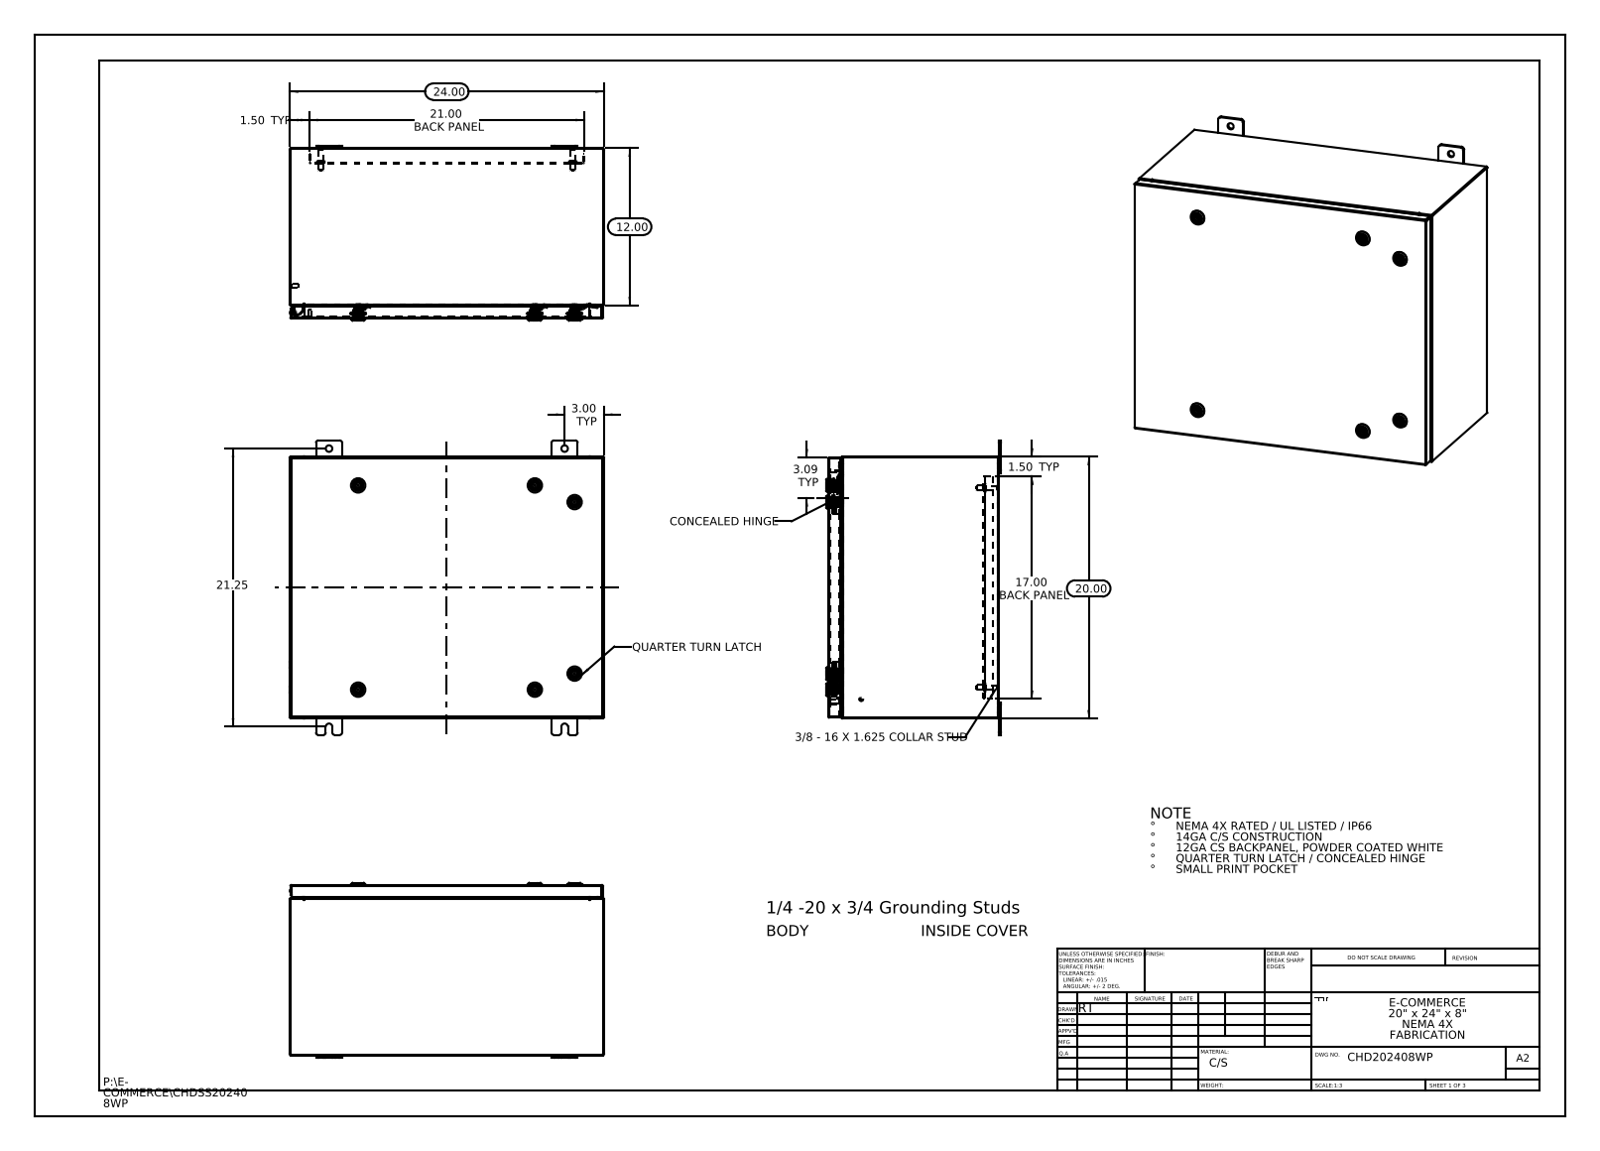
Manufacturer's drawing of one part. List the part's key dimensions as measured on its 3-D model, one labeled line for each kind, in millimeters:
Part name (STEP PRODUCT): HW-CLH-R001-0500_2412-026240-2445-Industrilas; Nut-211301-IB-Industrilas_Nut-211301-IB-Industrilas; HW-CLH-E5-8004_Cam-232112-U-Industrilas; CHDSS202408WP Body (+8 more)
STEP written by: SolidWorks 2013 (CONFIG_CONTROL_DESIGN)
Units: millimetres
Bodies: 55 solids, 5420 faces (1592 planar, 1692 cylindrical, 2136 other)
Overall size (bounding box): 609.6 × 571.5 × 339.2
Volume: 3 520 000 mm³ · Surface area: 3 497 000 mm²
Round holes (diameter × count): ⌀12.7 ×8, ⌀5 ×6, ⌀10 ×6, ⌀10.2 ×6, ⌀16 ×6, ⌀20 ×6, ⌀3.5 ×4, ⌀5.4 ×2
Round bosses / shafts (diameter × count): ⌀6 ×8, ⌀28 ×6, ⌀19.8 ×6, ⌀15.9 ×6, ⌀15.5 ×6, ⌀13.5 ×6, ⌀10 ×6, ⌀2.9 ×6
Partial cylindrical surfaces — rounded edges, fillets, slot ends (radius × count): R0.2 ×198, R3 ×198, R0.7 ×72, R0.5 ×24, R4.8 ×24, R5 ×24, R0.3 ×20, R2.2 ×18
Main face-to-face distances: 1.9, 506.1, 1.9, 607.7, 330.5, 328.5, 328.6, 326.7, 2.6, 25.4
Hole centre spacings: 47.2, 342.9, 387.4, 396.2, 432.1, 457.2, 463.8, 489
